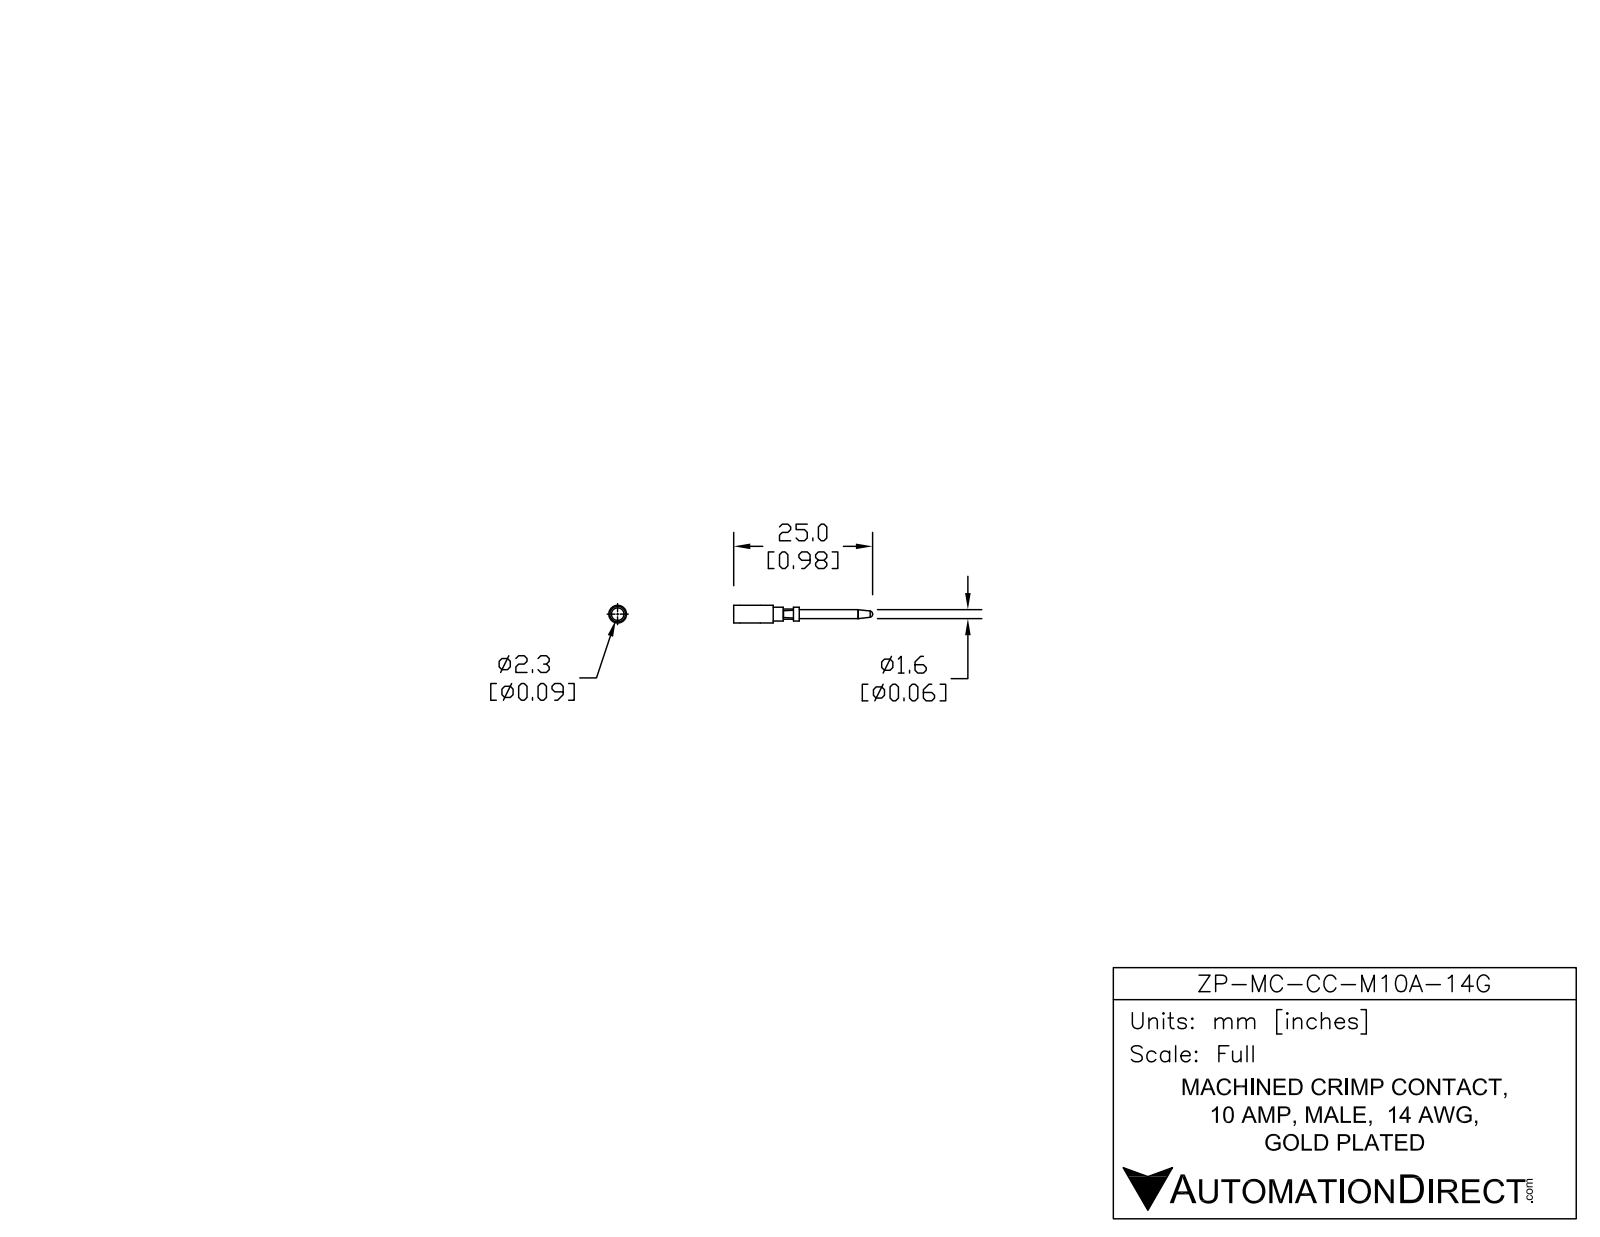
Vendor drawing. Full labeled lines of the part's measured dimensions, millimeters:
Part name (STEP PRODUCT): ZP-MC-CC-M10A-14G
STEP written by: SolidWorks 2014 (AUTOMOTIVE_DESIGN)
Units: millimetres
Bodies: 1 solid, 43 faces (13 planar, 15 cylindrical, 15 other)
Overall size (bounding box): 25 × 3.2 × 3.2
Volume: 78 mm³ · Surface area: 236 mm²
Round holes (diameter × count): ⌀0.8 ×1, ⌀2.25 ×1
Round bosses / shafts (diameter × count): ⌀3.2 ×1, ⌀2.48 ×1, ⌀1.6 ×1
Main face-to-face distances: 0.62, 7.12, 6.5, 1.84, 4.78, 5.4, 11.9, 2.98, 1.8, 2.42
